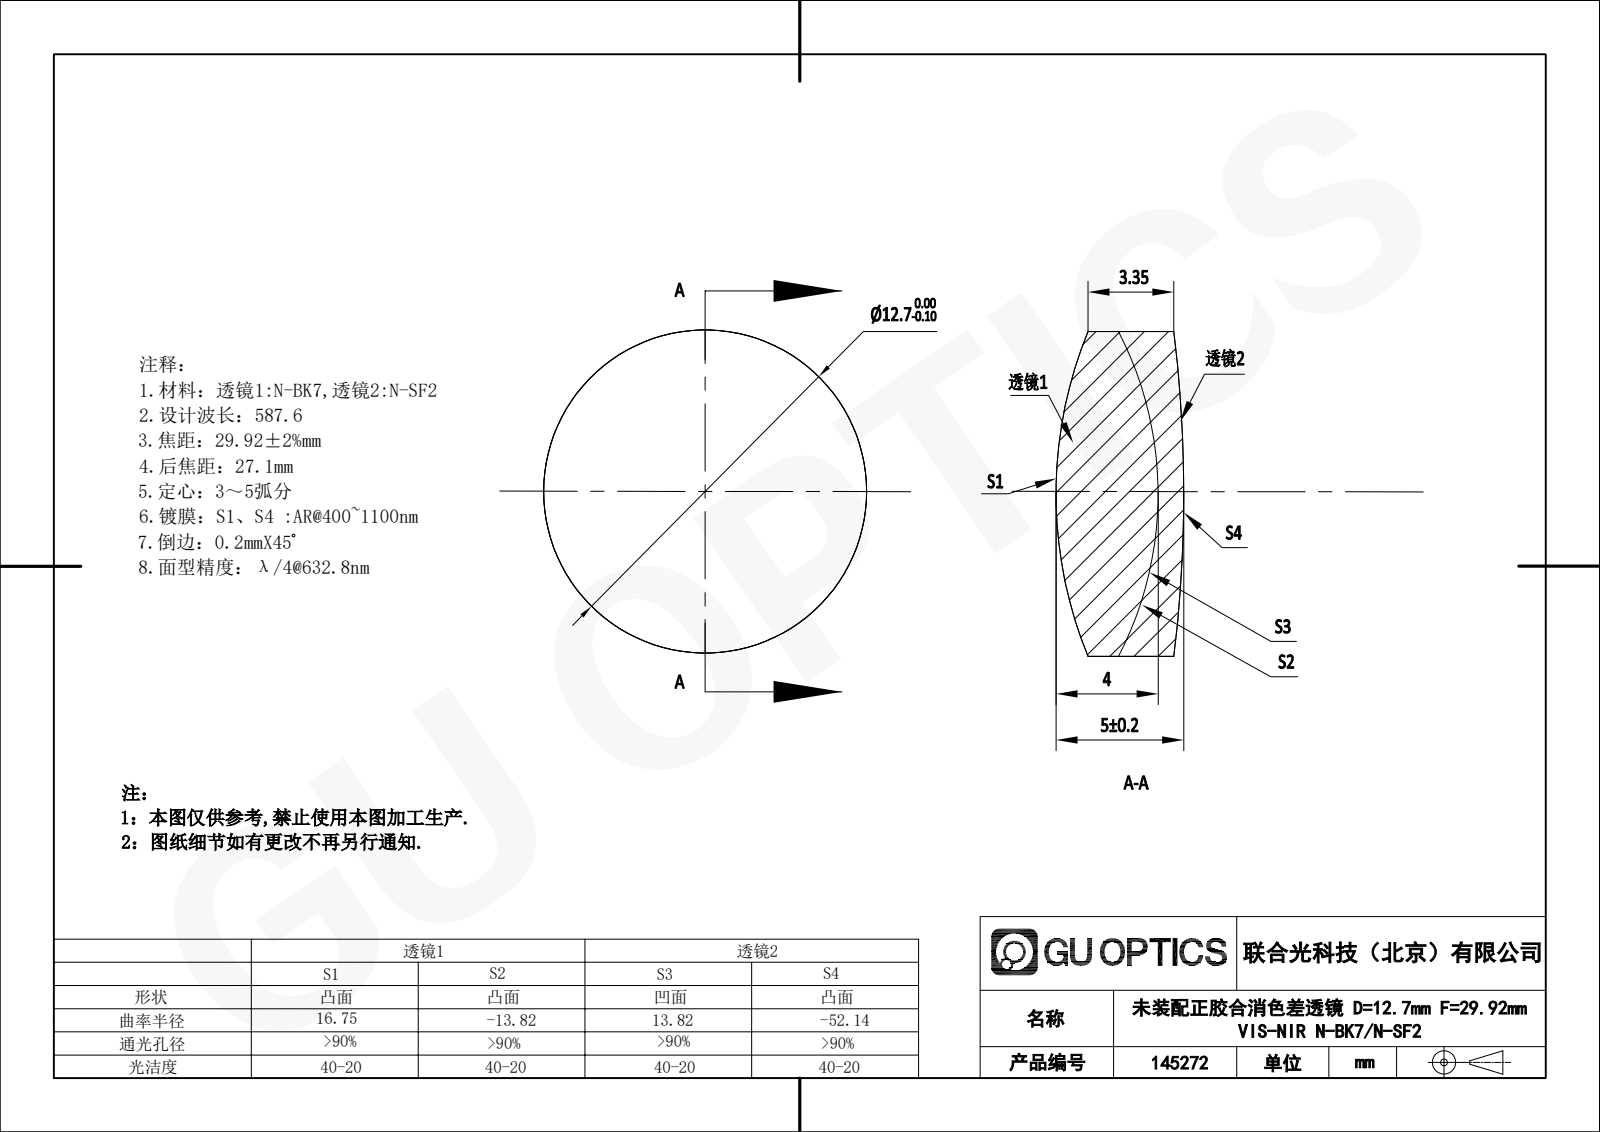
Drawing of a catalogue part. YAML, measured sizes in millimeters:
part_name: "145272"
step_written_by: "SolidWorks 2020 (CONFIG_CONTROL_DESIGN)"
units: millimeters
bodies: {solids: 2, faces: 12, planar: 0, cylindrical: 4, other: 8}
overall_size: [12.7, 12.7, 5]
volume: 531
surface_area: 661
round_bosses_or_shafts:
  - {diameter: 12.7, count: 1}
